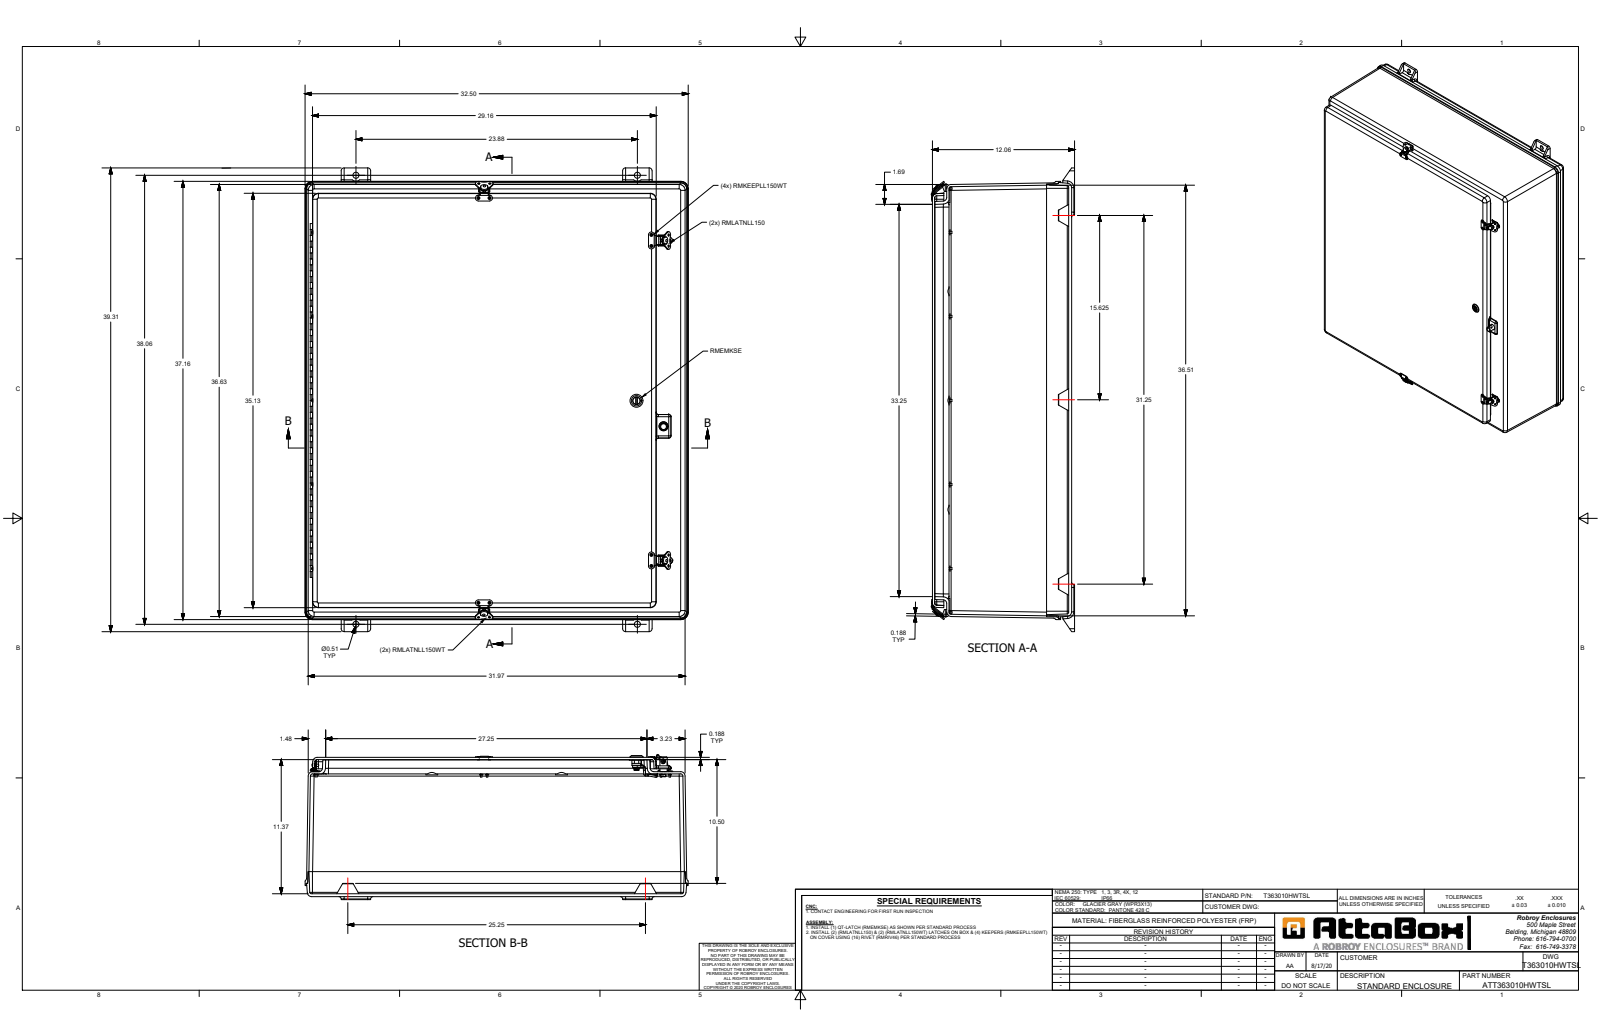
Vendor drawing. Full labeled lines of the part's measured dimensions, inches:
Part name (STEP PRODUCT): T363010HWTSL
STEP written by: SolidWorks 2019 (AUTOMOTIVE_DESIGN)
Units: inches
Bodies: 94 solids, 2137 faces (987 planar, 885 cylindrical, 265 other)
Overall size (bounding box): 39.313 × 32.5 × 12.307
Volume: 874.3 in³ · Surface area: 8 758 in²
Round holes (diameter × count): ⌀0.201 ×15, ⌀0.1 ×12, ⌀0.133 ×12, ⌀0.14 ×10, ⌀0.104 ×8, ⌀0.13 ×8, ⌀0.187 ×8, ⌀0.075 ×5, ⌀0.208 ×5, ⌀0.067 ×4, ⌀0.135 ×4, ⌀0.139 ×4
Round bosses / shafts (diameter × count): ⌀0.357 ×10, ⌀0.187 ×10, ⌀0.125 ×10, ⌀0.283 ×8, ⌀1 ×6, ⌀0.14 ×6, ⌀0.438 ×5, ⌀0.66 ×4
Partial cylindrical surfaces — rounded edges, fillets, slot ends (radius × count): R0.25 ×34, R0.015 ×32, R0.012 ×30, R0.06 ×19, R0.188 ×19, R0.011 ×16, R0.02 ×16, R0.07 ×16
Main face-to-face distances: 0.25, 0.188, 0.187, 11.809, 11.559, 11.621, 11.371, 0.188, 10.406, 10.156
Hole centre spacings: 14.25, 7.125, 7.125, 27.126, 21.375, 21.375, 28.5, 0.125
